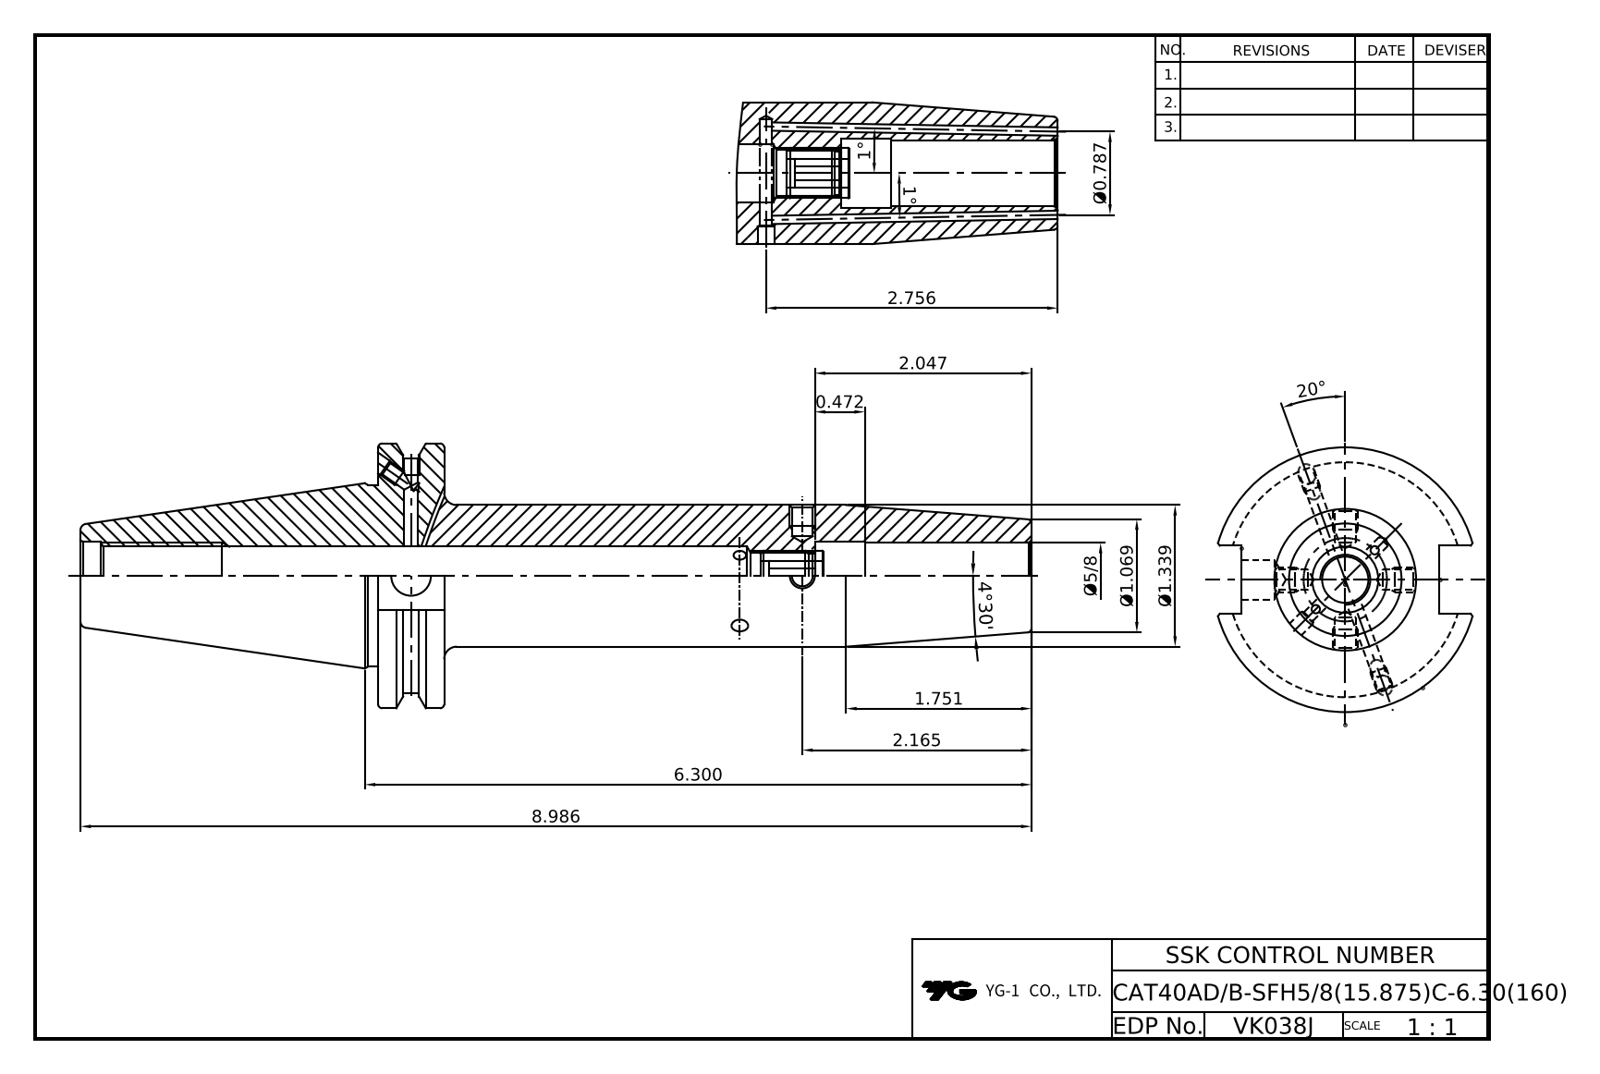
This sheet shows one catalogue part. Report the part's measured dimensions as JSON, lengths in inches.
{"part_name": "LO-CAT40ADB-SFH15.875C-160", "step_written_by": "Autodesk Inventor 2025 (AUTOMOTIVE_DESIGN)", "units": "inches", "bodies": {"solids": 1, "faces": 90, "planar": 37, "cylindrical": 30, "other": 23}, "overall_size": [8.986, 2.5, 2.405], "volume_in3": 12.29, "surface_area_in2": 64.04, "round_holes": [[0.128, 4], [0.098, 2], [0.157, 2], [0.165, 2], [0.375, 1], [0.43, 1], [0.527, 1], [0.625, 1], [0.642, 1], [0.672, 1]], "round_bosses_or_shafts": [[2.5, 1], [1.717, 1], [1.339, 1]], "partial_cylinders_radius": [[1.108, 1]], "face_to_face_distances": [0.625, 6.174, 5.549, 1.874, 0.645, 2.812, 3.437, 8.986, 6.939, 4.127]}
